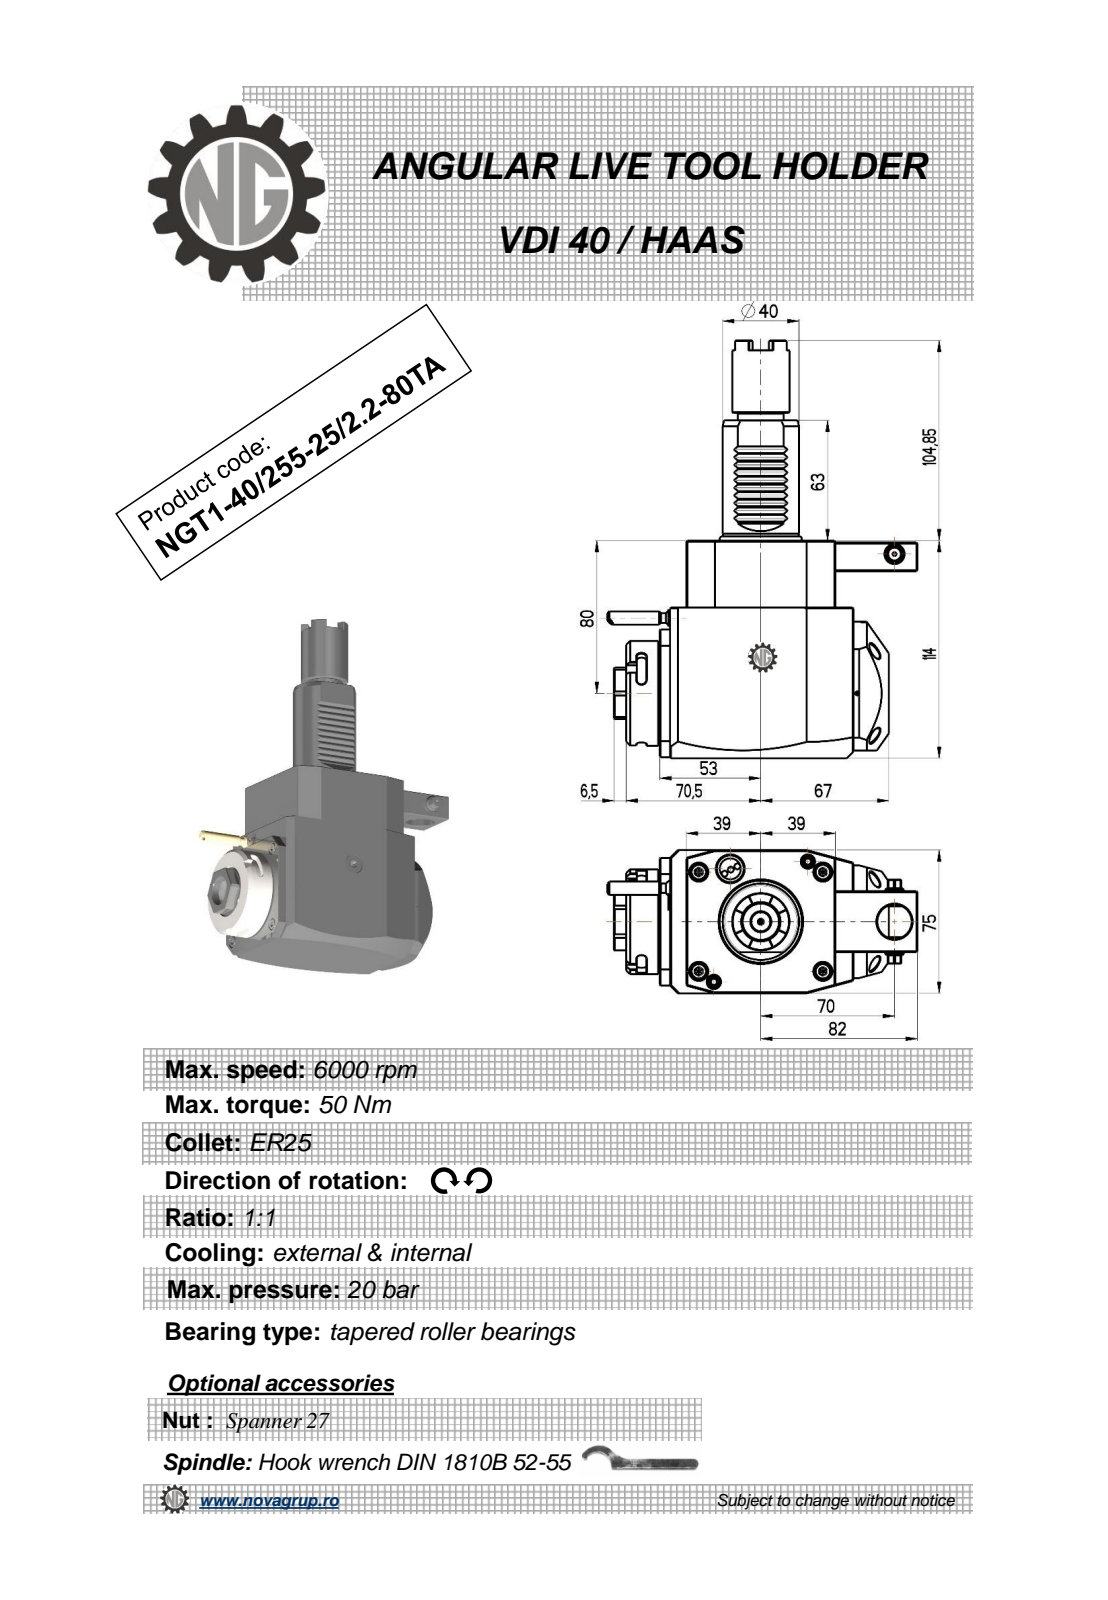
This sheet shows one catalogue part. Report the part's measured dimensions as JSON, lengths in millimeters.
{"part_name": "NGT1_40_255_25_1_2_80TA", "step_written_by": "PRO/ENGINEER BY PARAMETRIC TECHNOLOGY CORPORATION, 2010280 (CONFIG_CONTROL_DESIGN)", "units": "millimeters", "bodies": {"solids": 1, "faces": 391, "planar": 213, "cylindrical": 92, "other": 86}, "overall_size": [218.85, 162.33, 75], "volume_mm3": 988998, "surface_area_mm2": 76852, "round_holes": [[18, 2], [2, 1], [2.5, 1], [3, 1], [9.5, 1]], "round_bosses_or_shafts": [[8.96, 2], [55, 1], [48, 1], [40, 1], [30, 1], [20, 1], [10, 1], [7, 1]], "partial_cylinders_radius": [[0.3, 10], [2.5, 6], [180, 2], [0.5, 1], [3.85, 1], [4.25, 1], [15, 1], [24.5, 1]], "face_to_face_distances": [75, 114, 14, 17.5, 79, 109.5, 92, 78, 98, 31.5], "hole_center_spacings": [37.35, 43.2, 72.5]}
